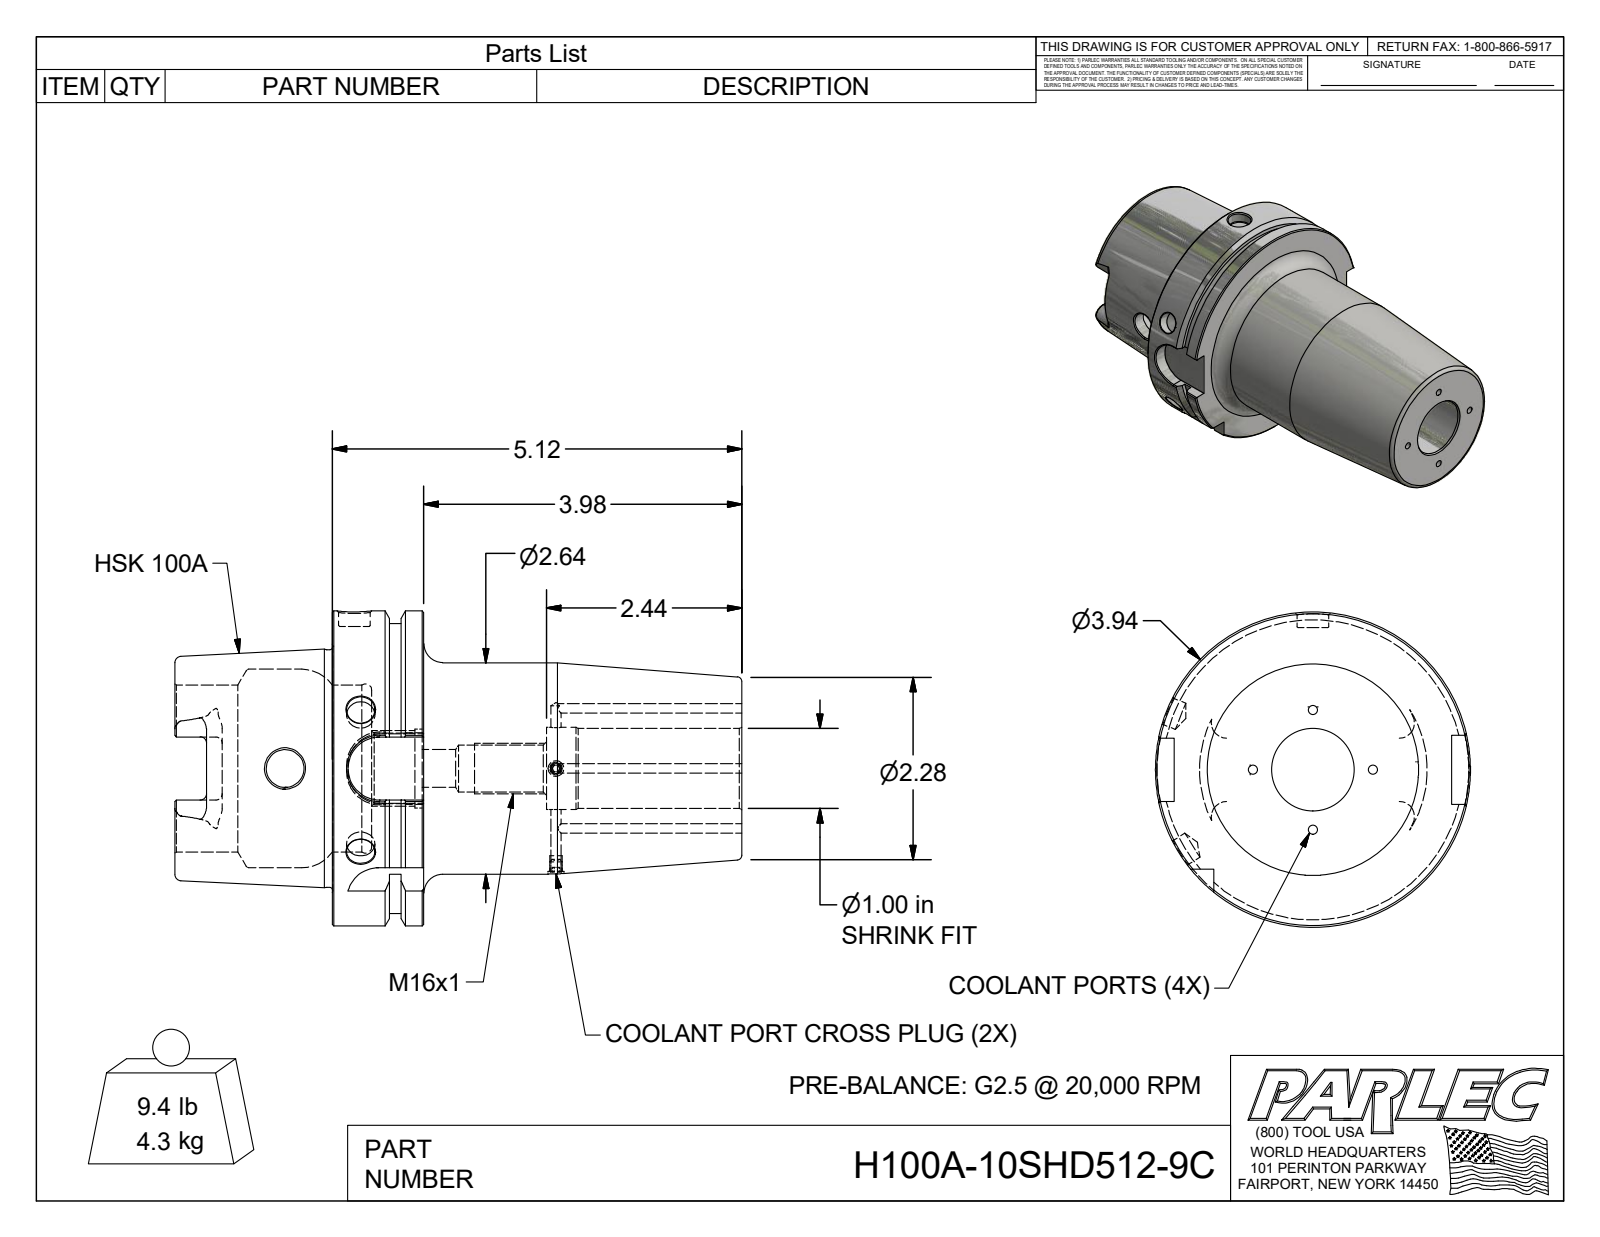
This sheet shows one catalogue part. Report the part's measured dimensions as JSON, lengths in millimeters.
{"part_name": "H100A-10SHD512-9C; 029-060", "step_written_by": "Autodesk Inventor 2018 (AUTOMOTIVE_DESIGN)", "units": "millimeters", "bodies": {"solids": 3, "faces": 171, "planar": 59, "cylindrical": 49, "other": 63}, "overall_size": [180, 100, 100], "volume_mm3": 545400, "surface_area_mm2": 78260, "round_holes": [[3, 4], [3.3, 2], [5, 2], [9, 2], [12, 2], [10, 1], [14.9, 1], [22.4, 1], [25, 1], [25.4, 1], [26.1, 1], [53, 1]], "round_bosses_or_shafts": [[4, 2], [100, 1], [92, 1], [75.4, 1], [67.1, 1]], "partial_cylinders_radius": [[2, 6], [4.9, 4], [10, 4]], "face_to_face_distances": [29, 130, 101, 12.5, 16.5, 117.5, 50, 62.5, 79, 180], "hole_center_spacings": [19, 26.9, 38, 64, 86]}
